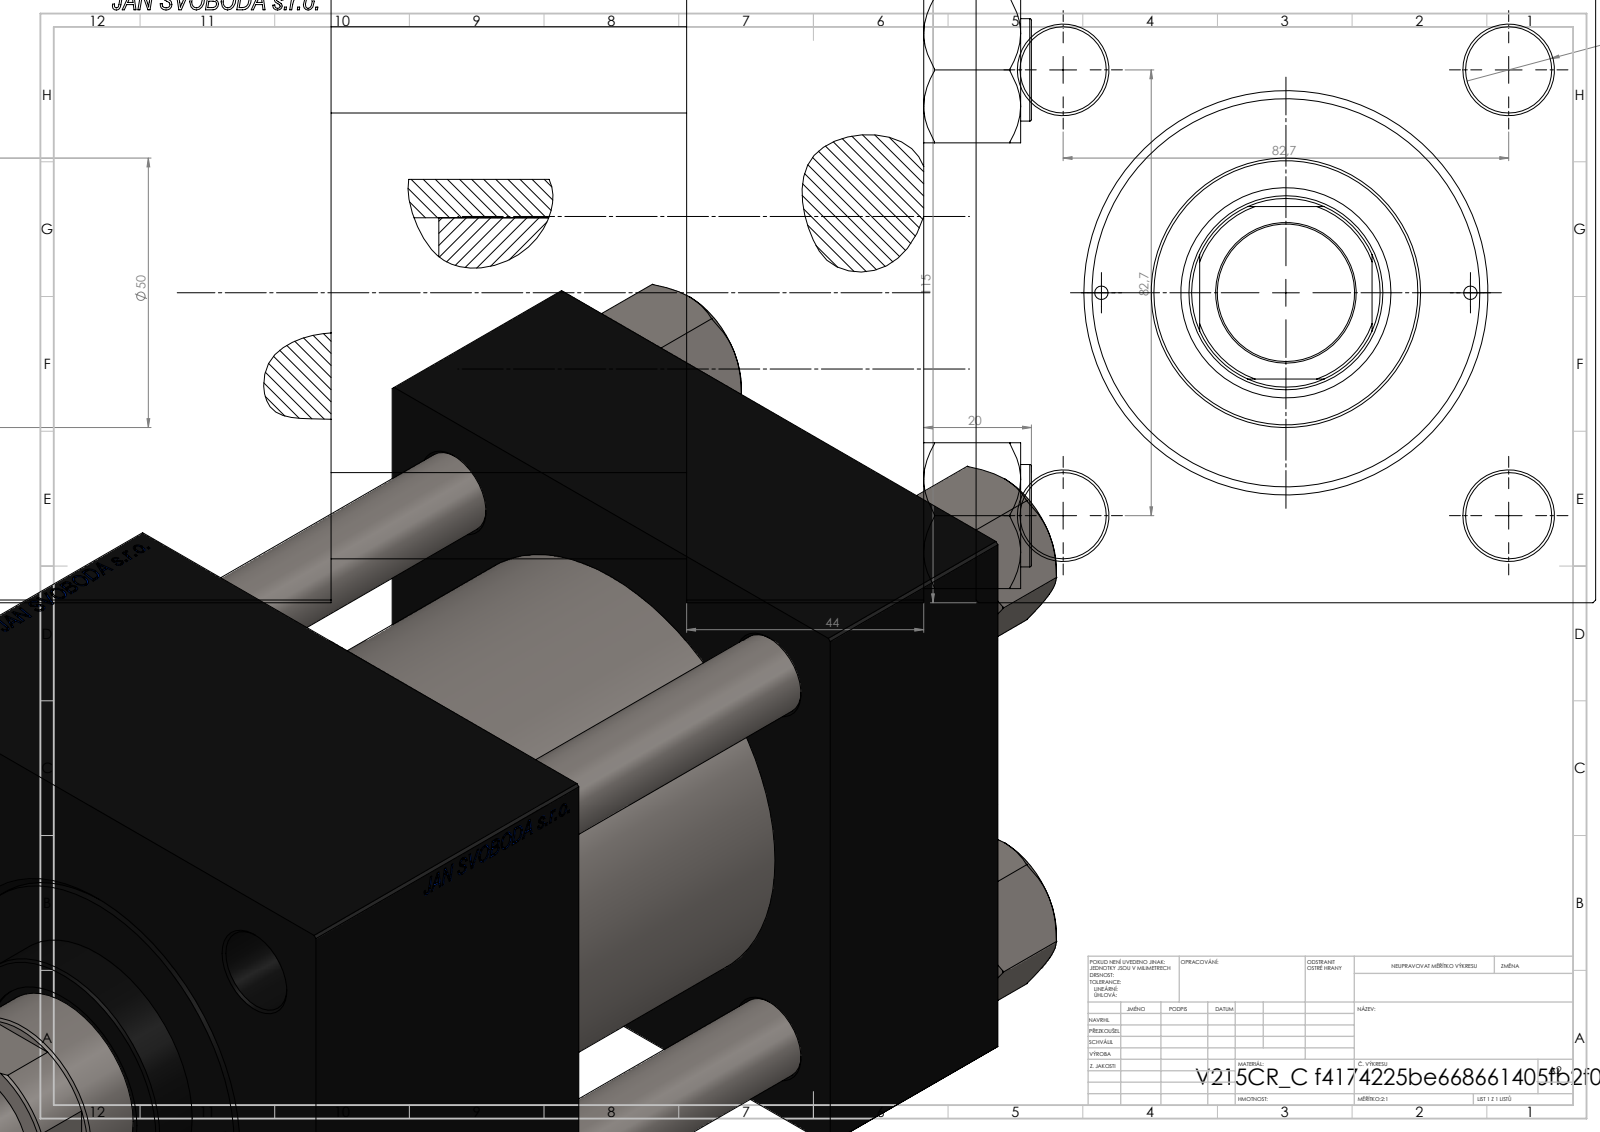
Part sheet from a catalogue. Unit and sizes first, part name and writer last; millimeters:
Units: millimetres
Overall size (bounding box): 230 × 113.94 × 109.75
Round holes (diameter × count): ⌀16 ×4, ⌀2.5 ×2, ⌀25.5 ×1, ⌀36 ×1, ⌀39 ×1
Round bosses / shafts (diameter × count): ⌀19 ×4, ⌀80 ×1, ⌀72 ×1, ⌀50 ×1
Partial cylindrical surfaces — rounded edges, fillets, slot ends (radius × count): R17.5 ×1
Main face-to-face distances: 46, 106.3, 60.3, 135, 89, 28.7, 71.62, 27.05, 41.35, 44
Hole centre spacings: 41.96, 58.48, 82.7, 86.17, 34.25, 116.96, 68.5
Volume: 570 234 mm³ · Surface area: 101 533 mm²
Bodies: 10 solids, 263 faces (109 planar, 46 cylindrical, 108 other)
Part name (STEP PRODUCT): V215CR_VCP_C; V215_VC_A; NUT_M5_C; V215CR_C_TYCINKA (+1 more)
STEP written by: SolidWorks 2019 (CONFIG_CONTROL_DESIGN)
